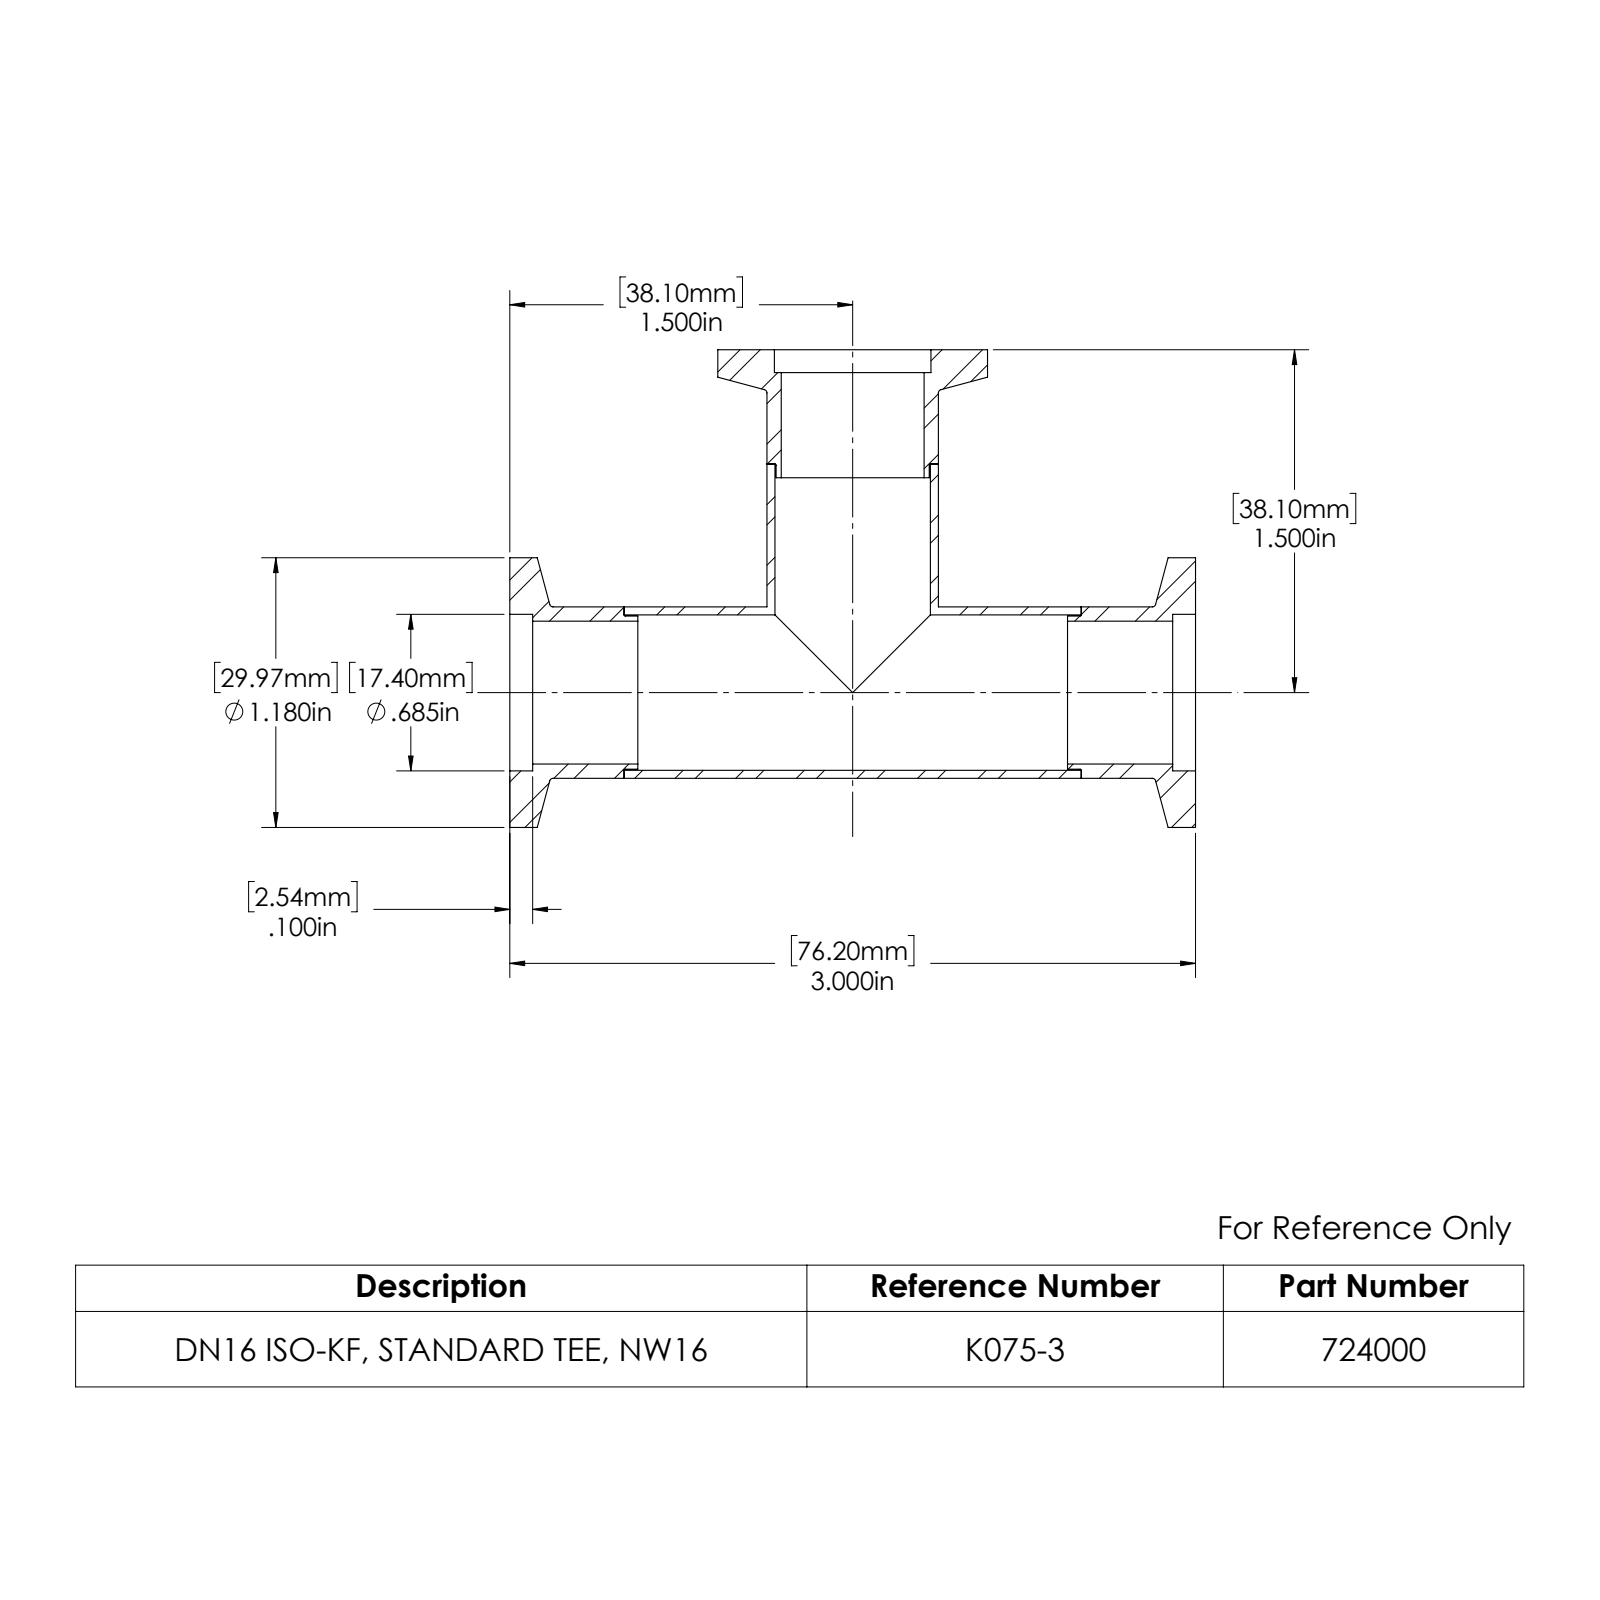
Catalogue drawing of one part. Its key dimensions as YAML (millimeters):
part_name: "713001; 724000_A; 404500"
step_written_by: "SolidWorks 2022 (CONFIG_CONTROL_DESIGN)"
units: millimeters
bodies: {solids: 4, faces: 71, planar: 15, cylindrical: 38, other: 18}
overall_size: [76.2, 53.1, 30]
volume: 11100
surface_area: 15330
round_holes:
  - {diameter: 15.9, count: 2}
  - {diameter: 17.3, count: 2}
  - {diameter: 17.4, count: 2}
round_bosses_or_shafts:
  - {diameter: 30, count: 2}
  - {diameter: 19.1, count: 2}
  - {diameter: 17, count: 2}
face_to_face_distances: [76.2, 12.7, 63.5, 2.5, 10.2, 50.8, 73.7, 61, 1.5, 11.7]
